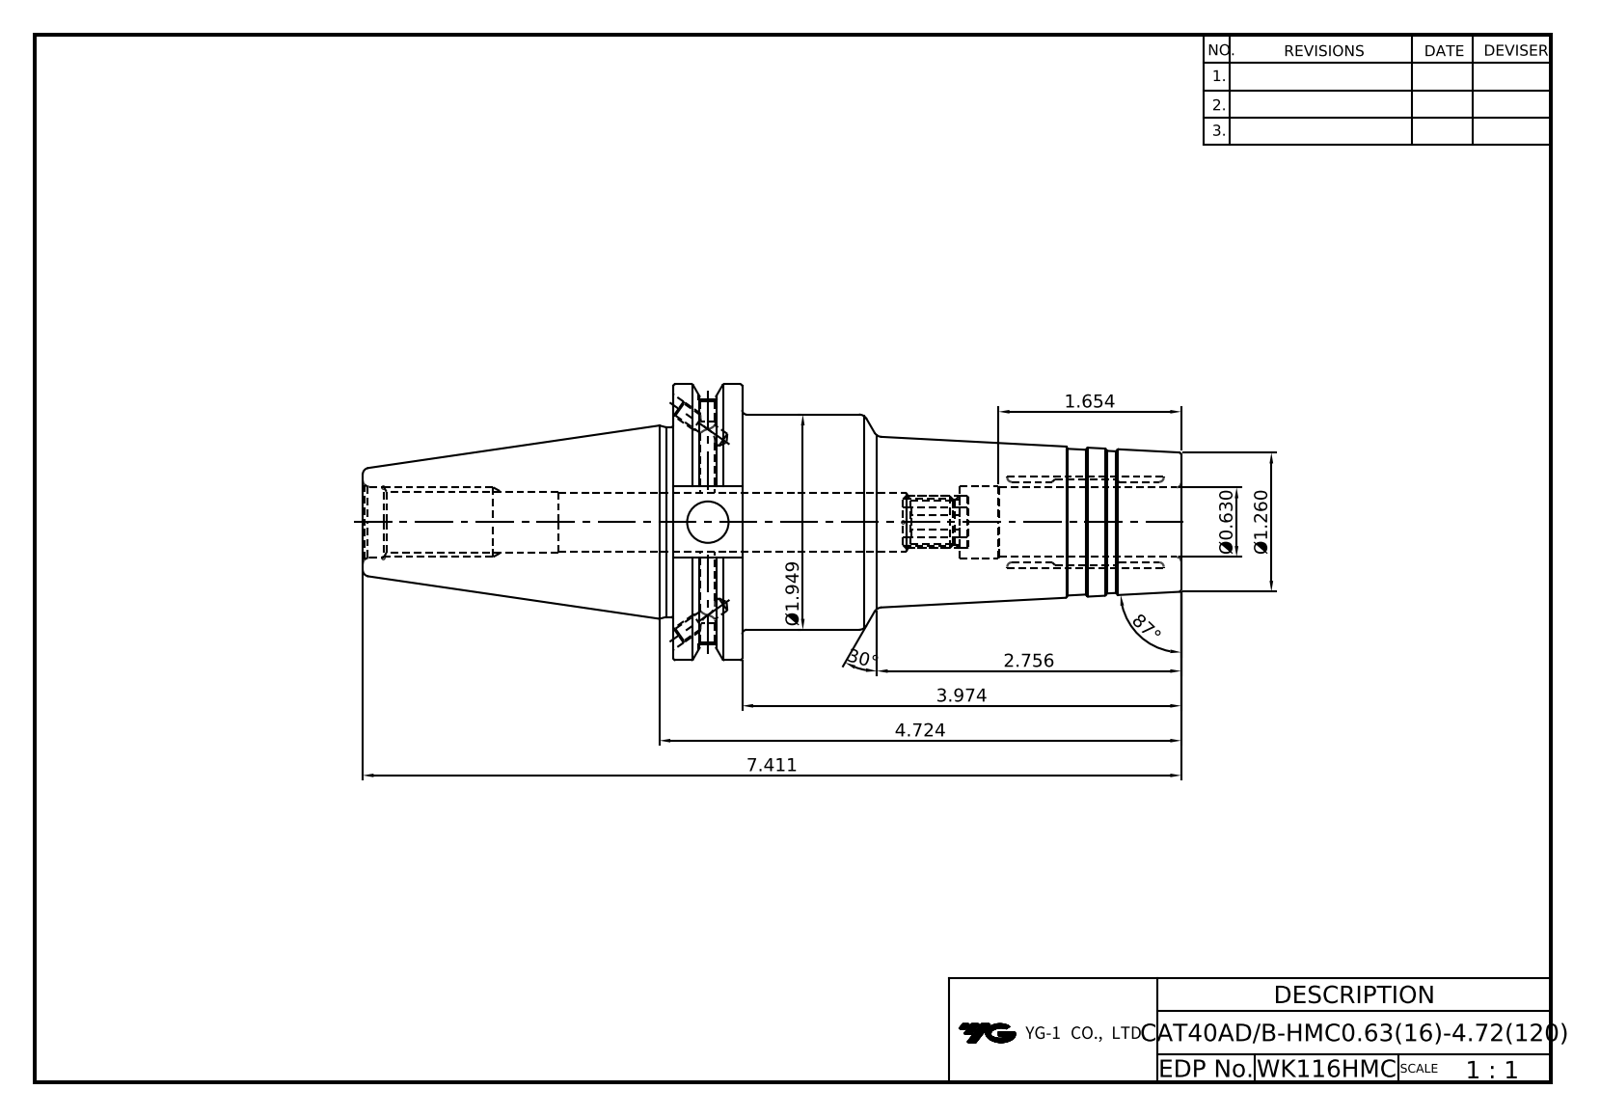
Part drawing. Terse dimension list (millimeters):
name: LO-CAT40ADB-HMC16-120
written by: Autodesk Inventor 2020 (AUTOMOTIVE_DESIGN)
unit: mm
bodies: 1 solid, 106 faces (36 planar, 30 cylindrical, 40 other)
size: 188.25 × 63.5 × 61.09
volume: 212 423 mm³; area: 37 187 mm²
holes: 4× ⌀3.24, 2× ⌀4, 2× ⌀4.2, 1× ⌀9.53, 1× ⌀10.92, 1× ⌀13, 1× ⌀13.39, 1× ⌀16, 1× ⌀16.3, 1× ⌀16.6
bosses: 1× ⌀63.5, 1× ⌀49.5, 1× ⌀43.6
rounds: 1× R8.19, 1× R28.15
face distances: 15.88, 116.83, 100.95, 47.6, 16.38, 71.42, 87.3, 188.25, 137.25, 65.83
